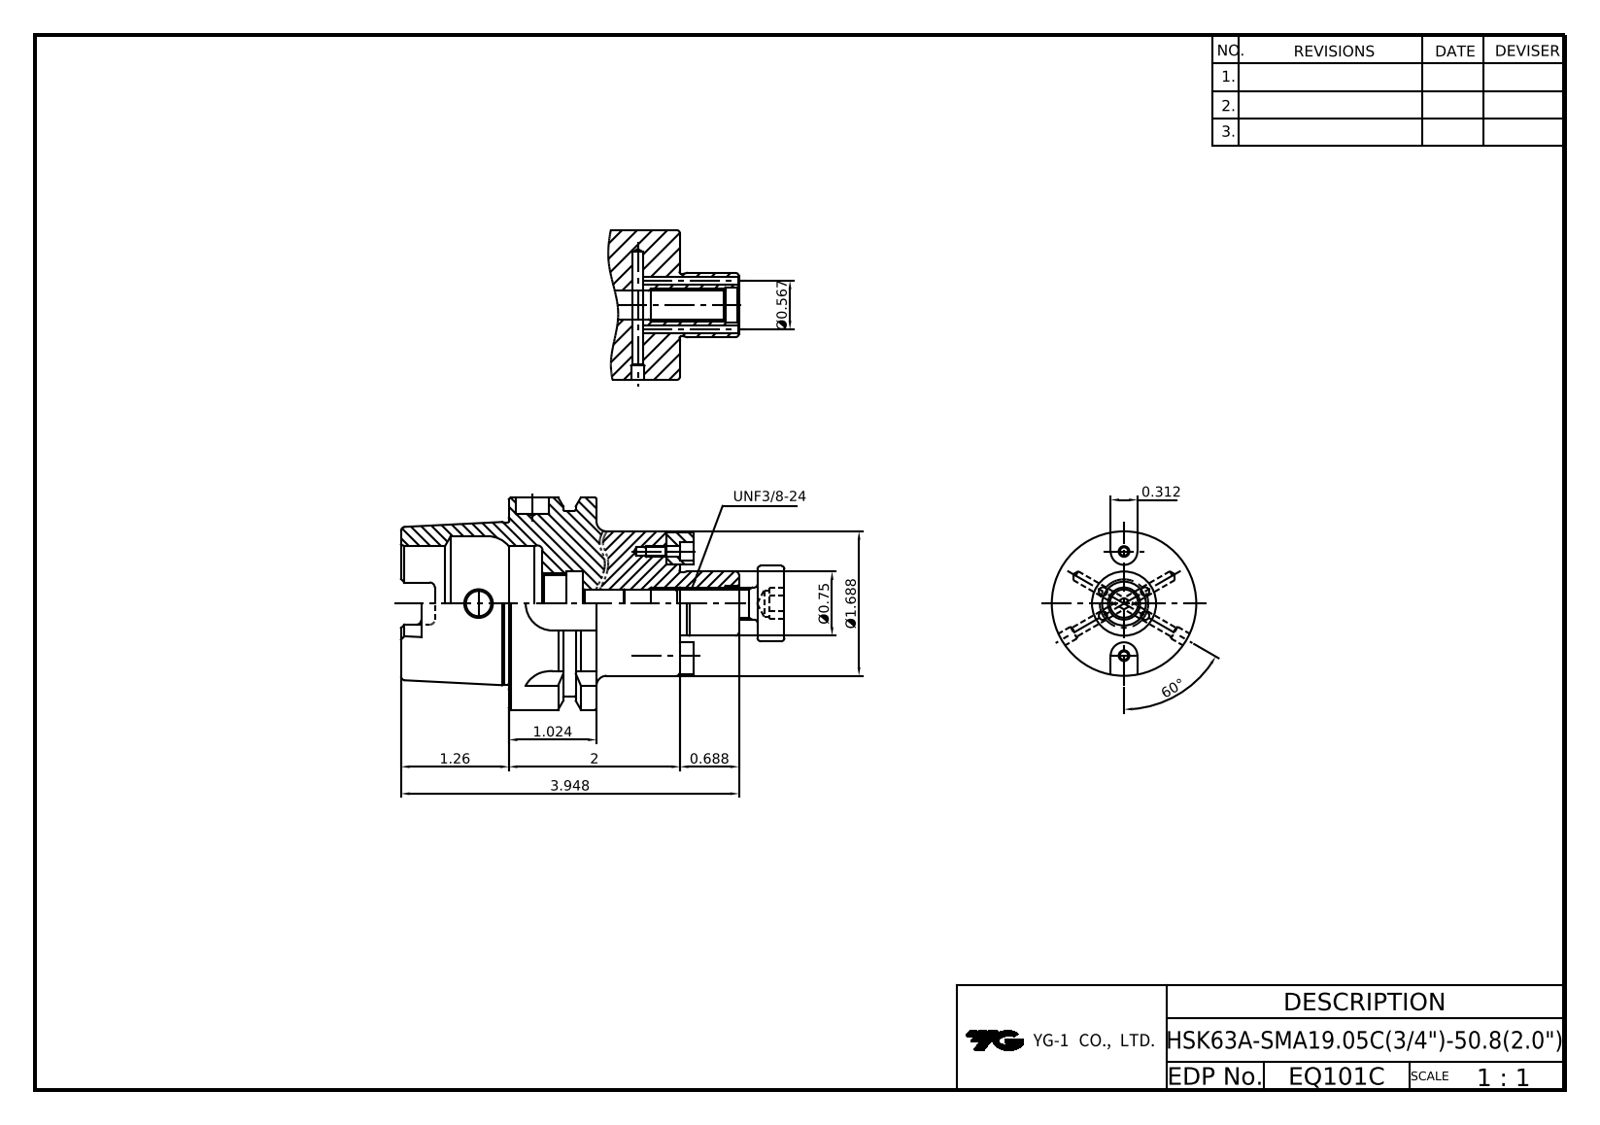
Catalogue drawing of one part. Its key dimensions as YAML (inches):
part_name: "LO-HSK63A-SMA19.05C-50.8; COLLAR BOLT-UNF3_8-24x24L; DRIVE KEY-7.93x7.93x9.5; HEX'' WRENCH BOLT-UNC#5-40x5_16L"
step_written_by: "Autodesk Inventor 2025 (AP242_MANAGED_MODEL_BASED_3D_ENGINEERING_MIM_LF)"
units: inches
bodies: {solids: 6, faces: 213, planar: 93, cylindrical: 56, other: 64}
overall_size: [4.657, 2.48, 2.48]
volume: 7.75
surface_area: 50.14
round_holes:
  - {diameter: 0.098, count: 4}
  - {diameter: 0.098, count: 2}
  - {diameter: 0.13, count: 2}
  - {diameter: 0.213, count: 2}
  - {diameter: 0.394, count: 2}
  - {diameter: 0.295, count: 1}
  - {diameter: 0.313, count: 1}
  - {diameter: 0.315, count: 1}
  - {diameter: 0.33, count: 1}
  - {diameter: 0.666, count: 1}
  - {diameter: 0.748, count: 1}
  - {diameter: 1.339, count: 1}
round_bosses_or_shafts:
  - {diameter: 0.205, count: 2}
  - {diameter: 0.125, count: 2}
  - {diameter: 2.48, count: 1}
  - {diameter: 2.165, count: 1}
  - {diameter: 1.891, count: 1}
  - {diameter: 1.75, count: 1}
  - {diameter: 0.882, count: 1}
  - {diameter: 0.75, count: 1}
partial_cylinders:
  - {radius: 0.059, count: 6}
  - {radius: 0.113, count: 4}
  - {radius: 0.156, count: 4}
  - {radius: 0.315, count: 4}
face_to_face_distances: [2, 1.024, 0.976, 0.394, 0.63, 1.606, 1.26, 0.157, 1.654, 2.283]
hole_center_spacings: [0.283, 0.537, 0.799, 0.491, 0.567, 0.619, 1.238]
